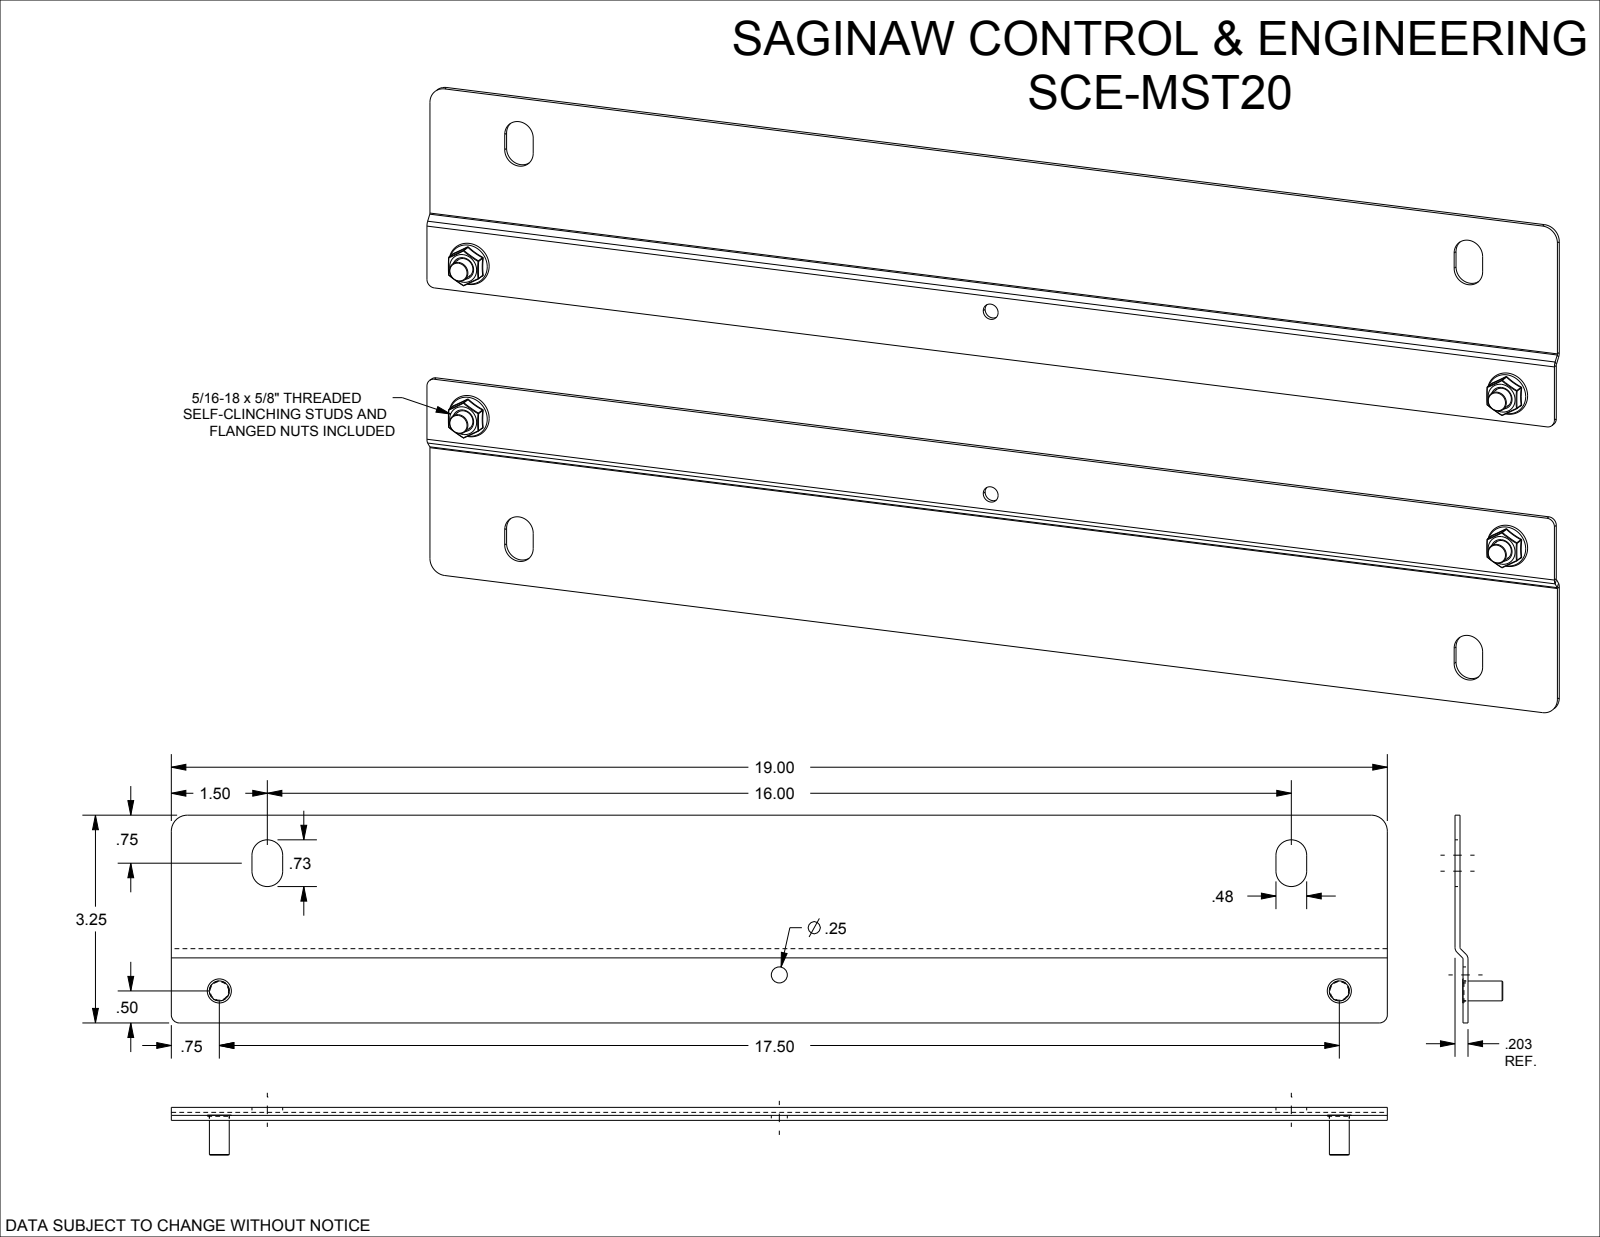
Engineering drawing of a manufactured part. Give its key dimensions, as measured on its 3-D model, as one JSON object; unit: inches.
{"part_name": "SCE-MST20", "step_written_by": "SolidWorks 2019 (AUTOMOTIVE_DESIGN)", "units": "inches", "bodies": {"solids": 10, "faces": 258, "planar": 72, "cylindrical": 66, "other": 120}, "overall_size": [19, 7.99, 0.746], "volume_in3": 10.02, "surface_area_in2": 263, "round_holes": [[0.312, 4], [0.25, 2]], "round_bosses_or_shafts": [[0.376, 4], [0.31, 4]], "partial_cylinders_radius": [[0.01, 24], [0.24, 8], [0.023, 4], [0.101, 4], [0.125, 4], [0.25, 4]], "face_to_face_distances": [0.078, 0.078, 0.125, 0.203, 0.047, 0.125, 3.245, 4.745, 1.5, 7.99], "hole_center_spacings": [8.754, 9.172, 2.5, 17.5, 17.678, 3]}
